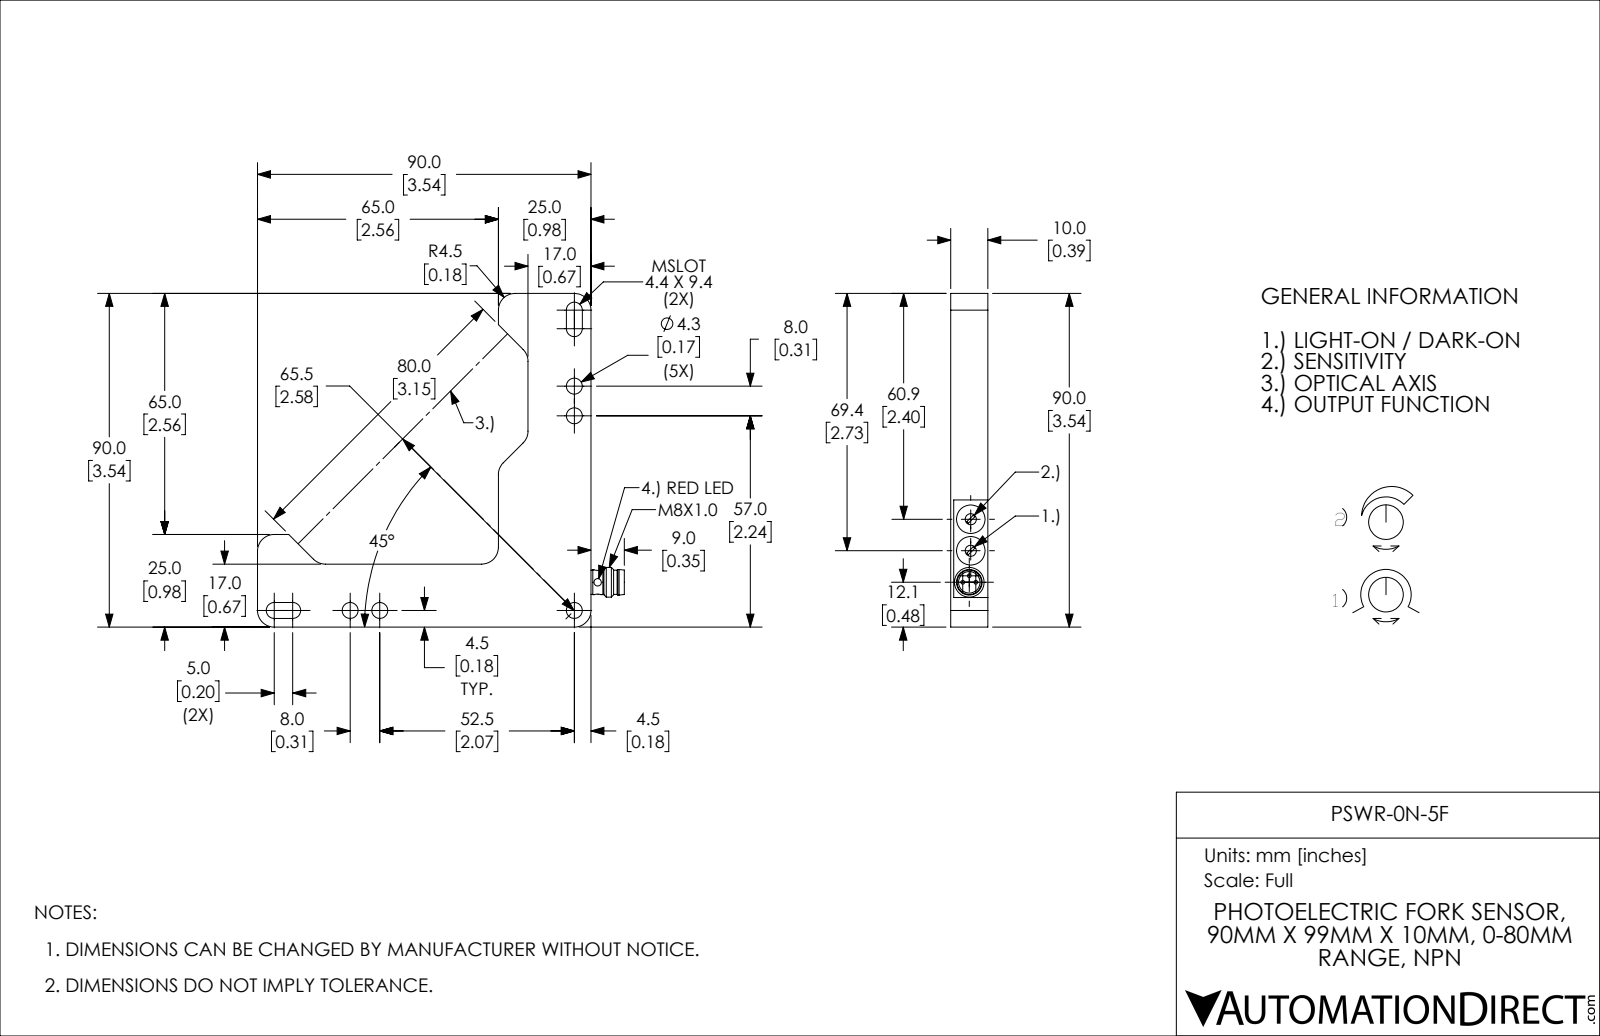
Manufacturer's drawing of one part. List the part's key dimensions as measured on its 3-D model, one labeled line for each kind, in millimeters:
Part name (STEP PRODUCT): PSWR-0N-5F
STEP written by: SolidWorks 2017 (AUTOMOTIVE_DESIGN)
Units: millimetres
Bodies: 1 solid, 90 faces (42 planar, 41 cylindrical, 7 other)
Overall size (bounding box): 99 × 90 × 10
Volume: 30 680 mm³ · Surface area: 11 280 mm²
Round holes (diameter × count): ⌀4.3 ×5, ⌀2 ×2, ⌀3 ×2, ⌀7.7 ×2, ⌀5.8 ×1
Round bosses / shafts (diameter × count): ⌀1 ×3, ⌀8 ×1, ⌀6.9 ×1, ⌀6.7 ×1, ⌀6.5 ×1
Partial cylindrical surfaces — rounded edges, fillets, slot ends (radius × count): R4.5 ×10, R2.2 ×4, R1.2 ×2
Main face-to-face distances: 10, 17, 90, 73, 25, 8, 65, 89.9, 24.9, 16.9
Hole centre spacings: 8, 52.5, 60.5, 80.1, 8.5, 8.5, 9.9, 17
